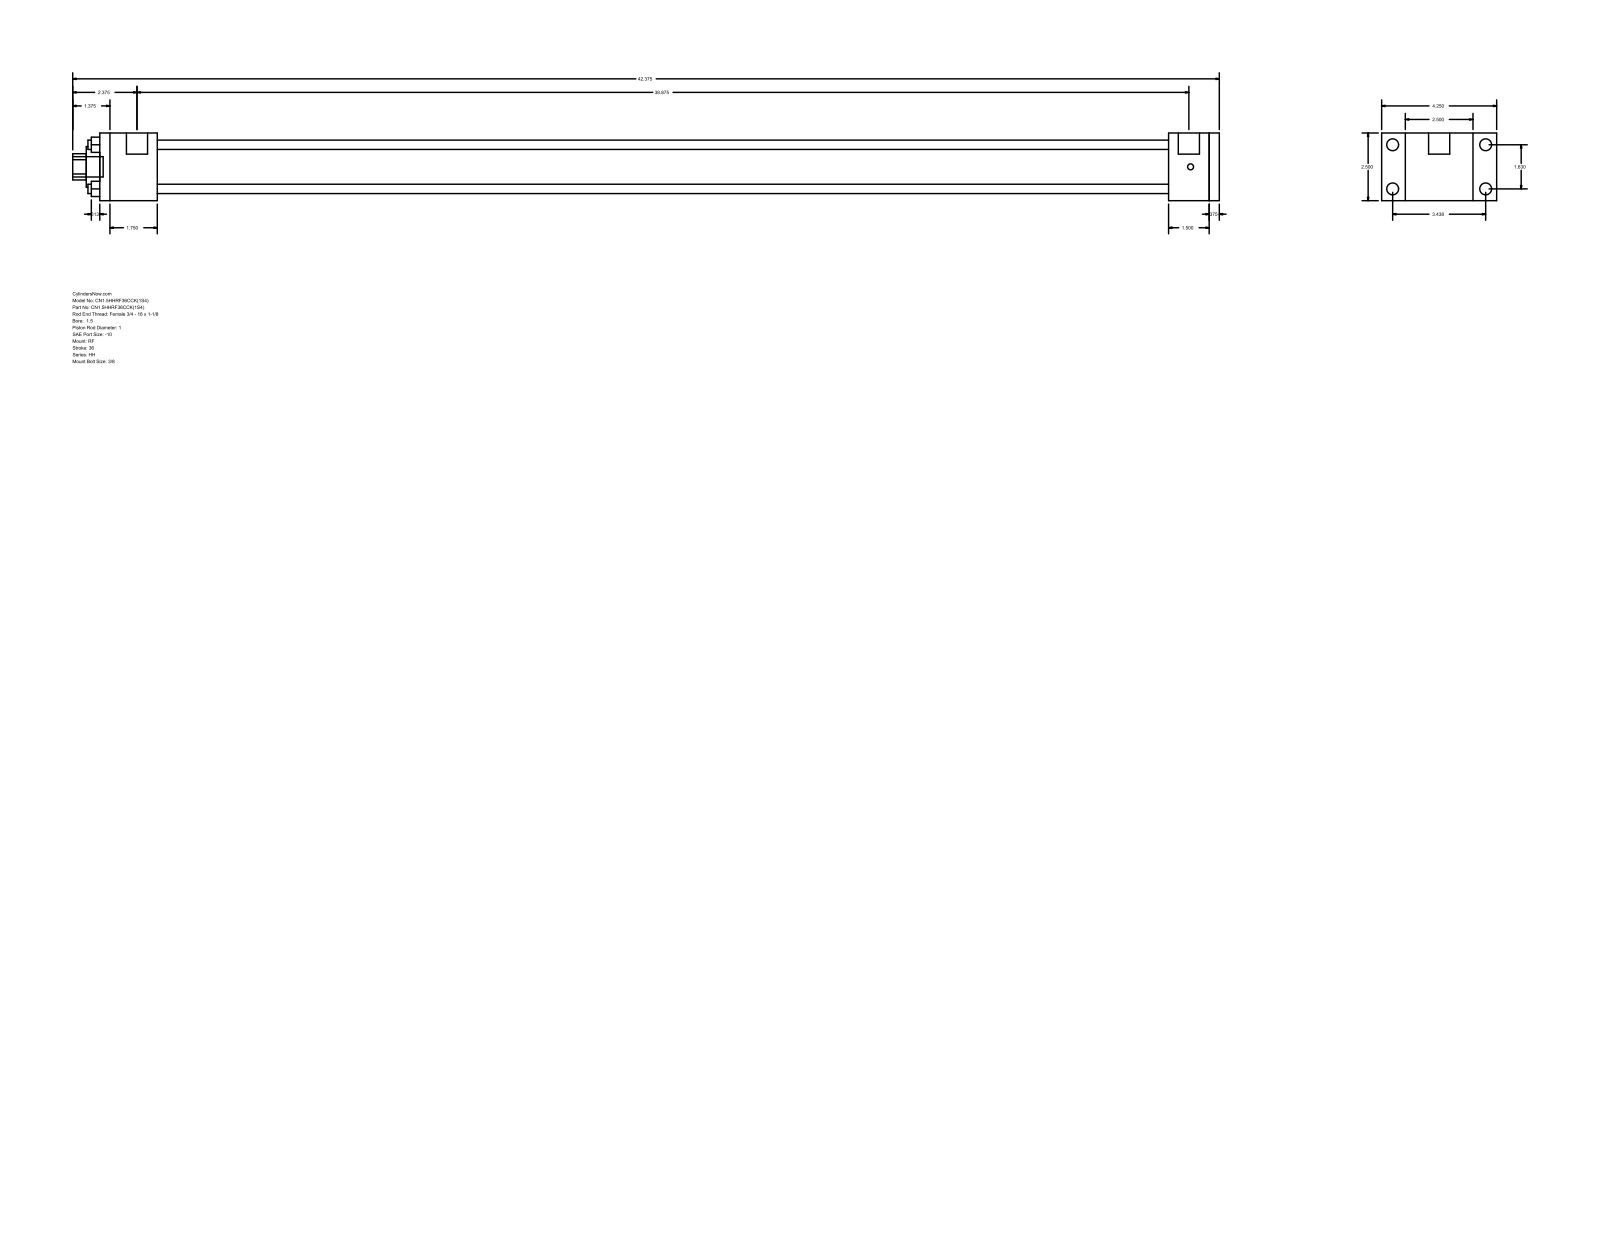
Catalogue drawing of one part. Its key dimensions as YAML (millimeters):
part_name: "HH_RF__0150_1"
step_written_by: "GSSL Pune (CONFIG_CONTROL_DESIGN)"
units: millimeters
bodies: {solids: 0, faces: 92, planar: 64, cylindrical: 28, other: 0}
overall_size: [1076.33, 107.95, 63.5]
round_holes:
  - {diameter: 8.76, count: 4}
  - {diameter: 25.4, count: 1}
  - {diameter: 38.1, count: 1}
  - {diameter: 44.45, count: 1}
round_bosses_or_shafts:
  - {diameter: 11.13, count: 4}
  - {diameter: 5.56, count: 4}
  - {diameter: 19.84, count: 2}
  - {diameter: 19.05, count: 1}
partial_cylinders:
  - {radius: 12.29, count: 1}
face_to_face_distances: [63.5, 9.53, 949.32, 987.42, 996.95, 38.1, 47.63, 53.98, 1003.3, 1041.4]
hole_center_spacings: [29.27, 41.4, 58.55]
